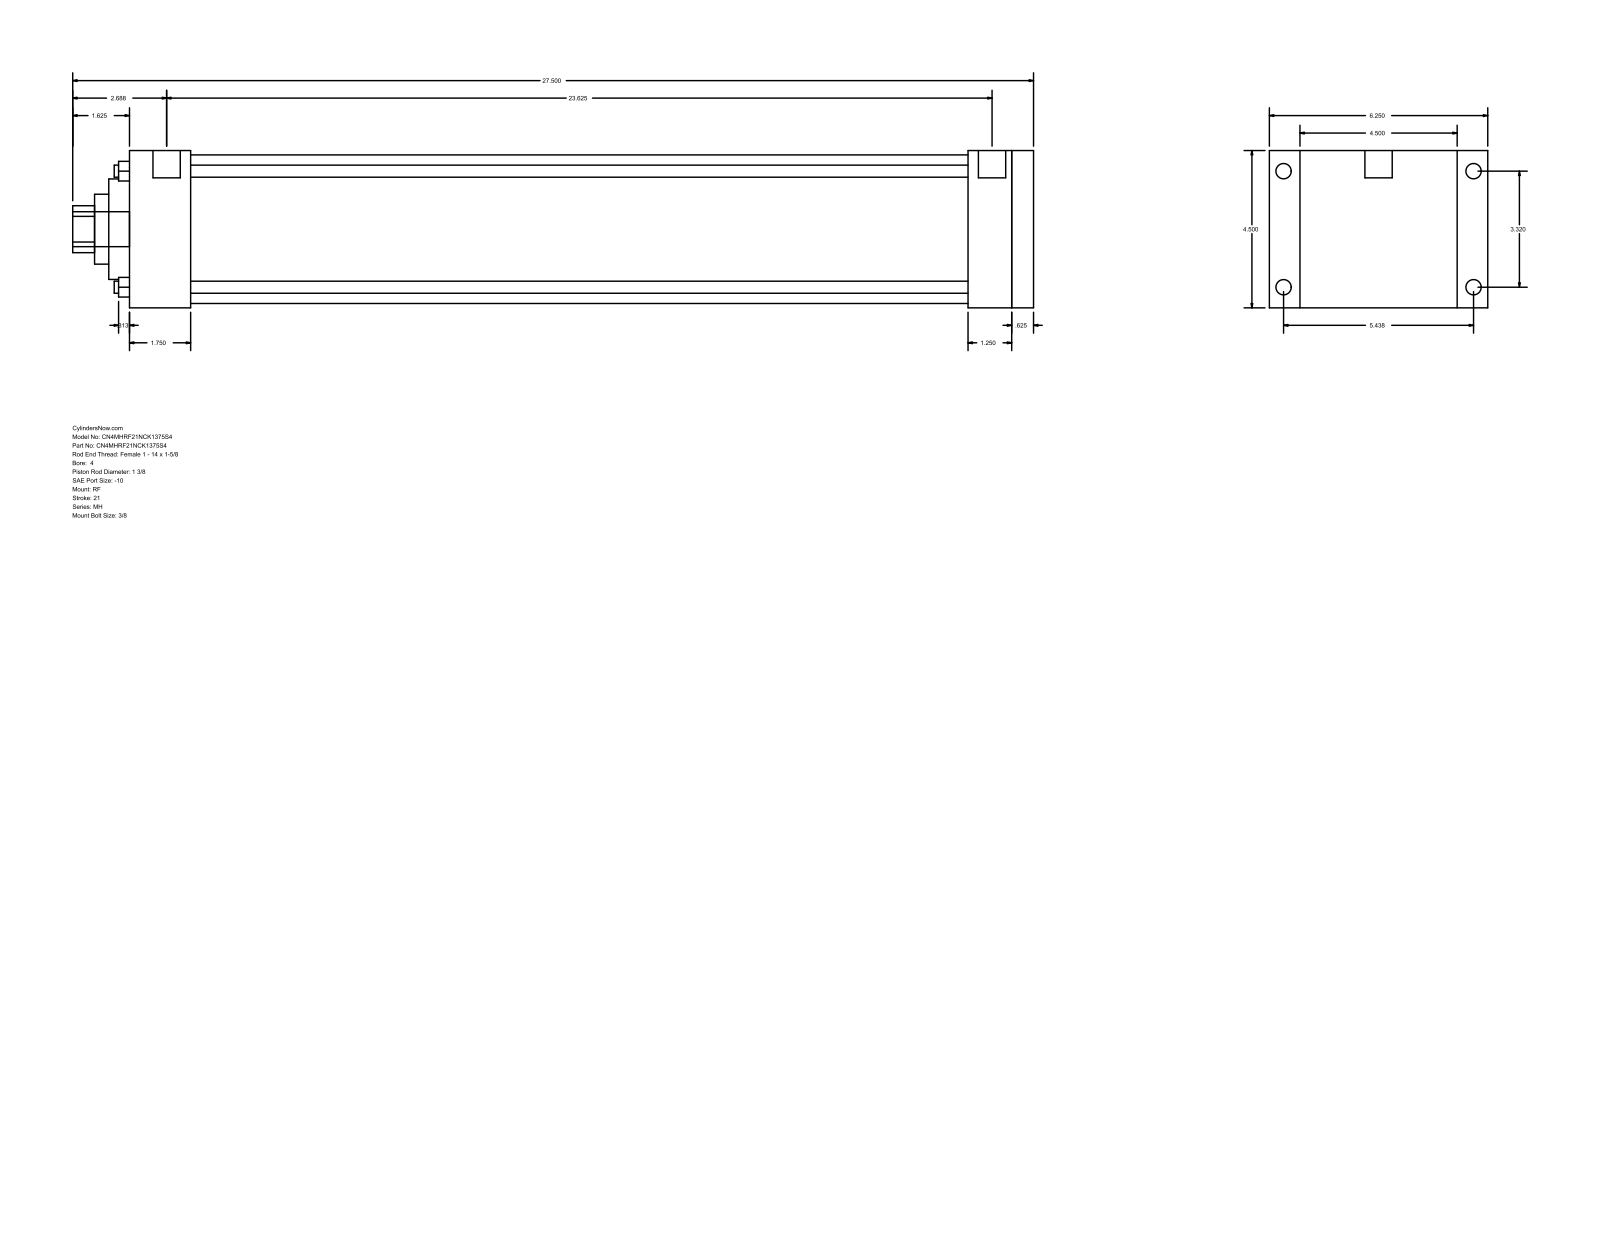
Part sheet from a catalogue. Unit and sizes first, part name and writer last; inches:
Units: inches
Overall size (bounding box): 27.5 × 6.25 × 4.5
Round holes (diameter × count): ⌀0.345 ×4, ⌀1.375 ×1, ⌀2 ×1, ⌀2.875 ×1, ⌀4.25 ×1
Round bosses / shafts (diameter × count): ⌀0.438 ×4, ⌀0.344 ×4, ⌀0.781 ×2, ⌀1 ×1
Partial cylindrical surfaces — rounded edges, fillets, slot ends (radius × count): R0.672 ×1
Main face-to-face distances: 4.5, 25.875, 0.625, 25.25, 1.75, 23.5, 24.125, 24, 22.25, 1.25
Hole centre spacings: 2.347, 3.32, 4.695
Bodies: 0 solids, 94 faces (65 planar, 29 cylindrical, 0 other)
Part name (STEP PRODUCT): MH_RF__0400_1.375
STEP written by: GSSL Pune (CONFIG_CONTROL_DESIGN)
